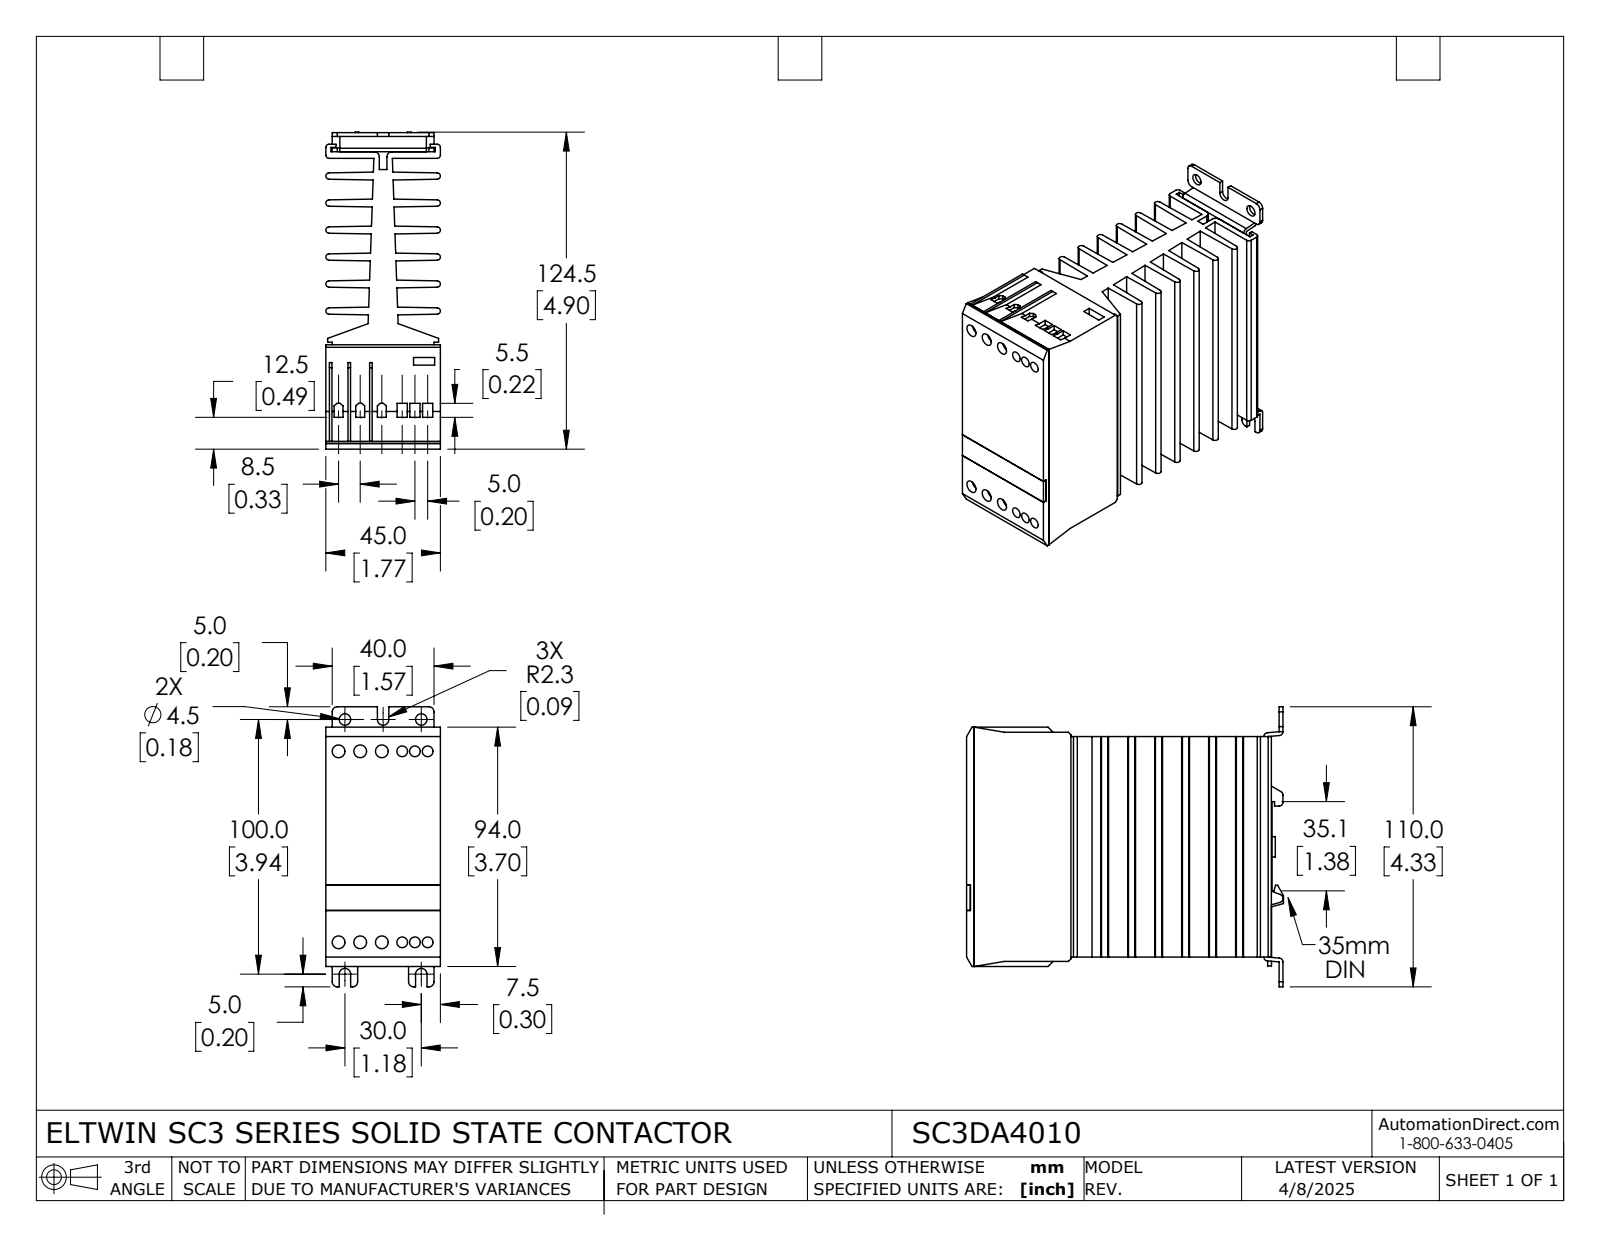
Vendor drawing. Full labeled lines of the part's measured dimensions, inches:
Part name (STEP PRODUCT): SC3DA4010
STEP written by: SolidWorks 2021 (AUTOMOTIVE_DESIGN)
Units: inches
Bodies: 5 solids, 427 faces (316 planar, 111 cylindrical, 0 other)
Overall size (bounding box): 4.902 × 4.331 × 1.772
Volume: 18.87 in³ · Surface area: 165.9 in²
Round holes (diameter × count): ⌀0.165 ×6, ⌀0.173 ×6, ⌀0.197 ×6, ⌀0.236 ×6, ⌀0.177 ×2
Round bosses / shafts (diameter × count): ⌀0.315 ×1
Partial cylindrical surfaces — rounded edges, fillets, slot ends (radius × count): R0.079 ×18, R0.049 ×16, R0.059 ×10, R0.051 ×4, R0.089 ×3
Main face-to-face distances: 0.417, 0.835, 0.127, 1.252, 0.29, 0.544, 0.707, 0.962, 1.669, 1.125
Hole centre spacings: 2.953, 0.197, 0.335, 2.959, 2.972, 0.502, 1.181, 3.446
